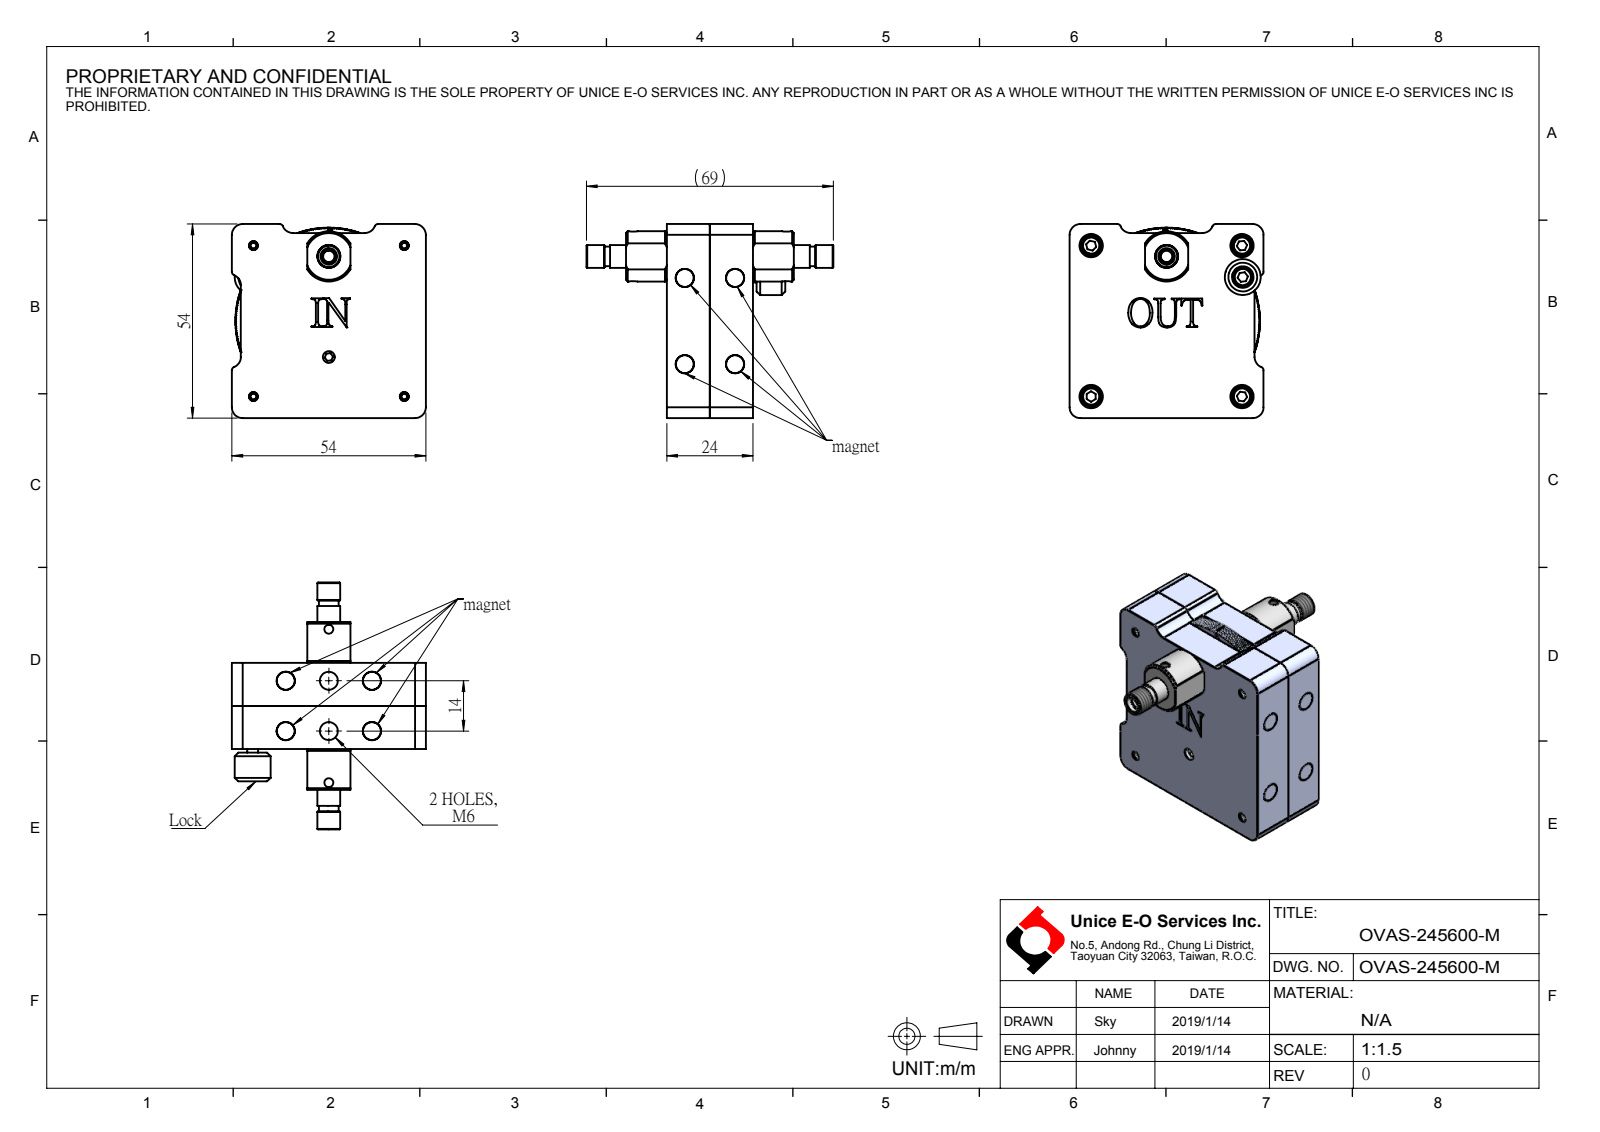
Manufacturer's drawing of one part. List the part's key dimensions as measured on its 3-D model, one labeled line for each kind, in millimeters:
Part name (STEP PRODUCT): OVAS-245600-M
STEP written by: SolidWorks 2022 (CONFIG_CONTROL_DESIGN)
Units: millimetres
Bodies: 0 solids, 236 faces (137 planar, 77 cylindrical, 22 other)
Overall size (bounding box): 68.76 × 54 × 54
Round holes (diameter × count): ⌀5.1 ×8, ⌀2.5 ×5, ⌀6.5 ×4, ⌀5 ×2, ⌀3.3 ×1, ⌀3.6 ×1, ⌀4.6 ×1, ⌀6 ×1, ⌀6.4 ×1
Round bosses / shafts (diameter × count): ⌀5 ×8, ⌀5.5 ×5, ⌀52 ×1, ⌀10 ×1, ⌀6.35 ×1, ⌀5.3 ×1
Partial cylindrical surfaces — rounded edges, fillets, slot ends (radius × count): R3 ×8, R1 ×4, R7 ×1
Main face-to-face distances: 24, 8.5, 15.5, 9.35, 0.85, 14.65, 54, 2.5, 51.5, 2.65
Hole centre spacings: 14, 12, 18.44, 18.71, 24, 27.78, 30.79, 42
